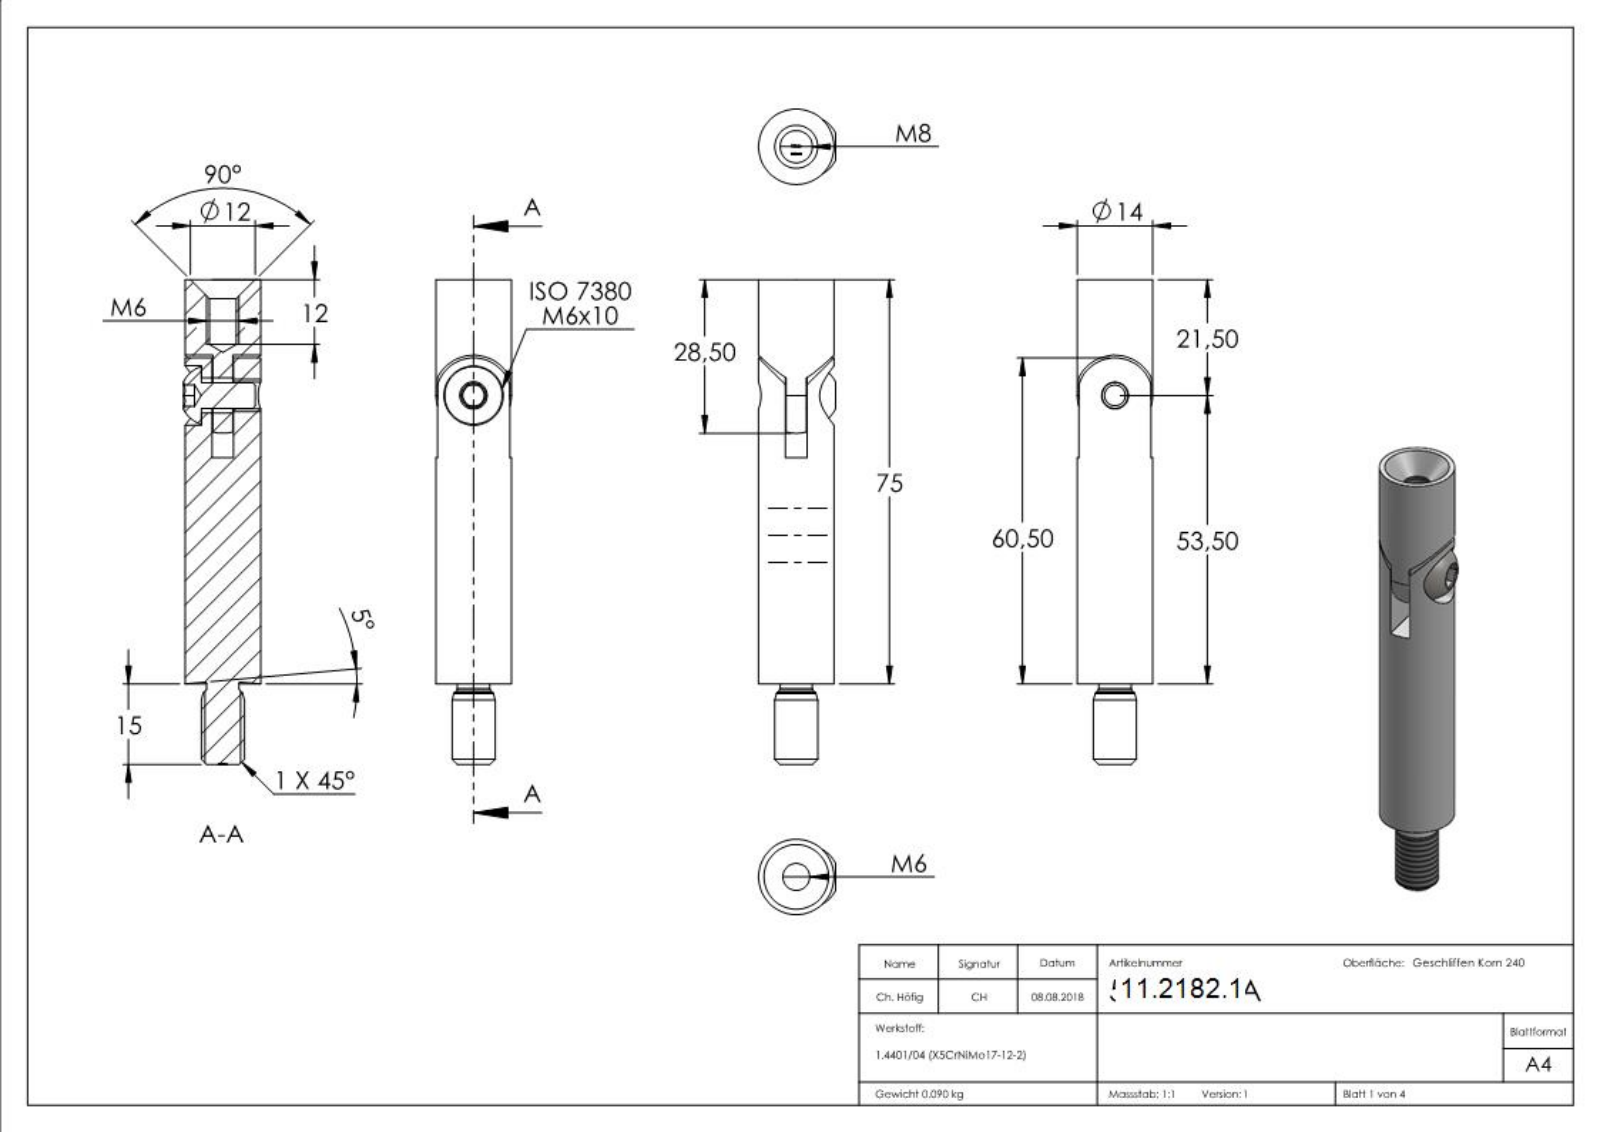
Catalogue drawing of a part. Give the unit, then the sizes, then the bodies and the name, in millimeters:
Units: millimetres
Overall size (bounding box): 90 × 14.3 × 14
Round holes (diameter × count): ⌀5 ×2, ⌀6.5 ×1, ⌀11 ×1
Round bosses / shafts (diameter × count): ⌀14 ×1, ⌀10.6 ×1, ⌀8 ×1, ⌀6 ×1, ⌀4.77 ×1
Partial cylindrical surfaces — rounded edges, fillets, slot ends (radius × count): R7 ×1, R7.5 ×1
Main face-to-face distances: 3.87, 4, 2, 6, 2.13, 5.87, 3.74, 33, 57, 90
Volume: 11 241 mm³ · Surface area: 5 661 mm²
Bodies: 3 solids, 303 faces (151 planar, 26 cylindrical, 126 other)
Part name (STEP PRODUCT): 50232-V4A; 50232-V4A Teil1_50232-V4A Teil1; 50232-V4A Teil3_ISO 7380 M6x10; 50232-V4A Teil2_50232-V4A Teil2
STEP written by: SolidWorks 2015 (CONFIG_CONTROL_DESIGN)
